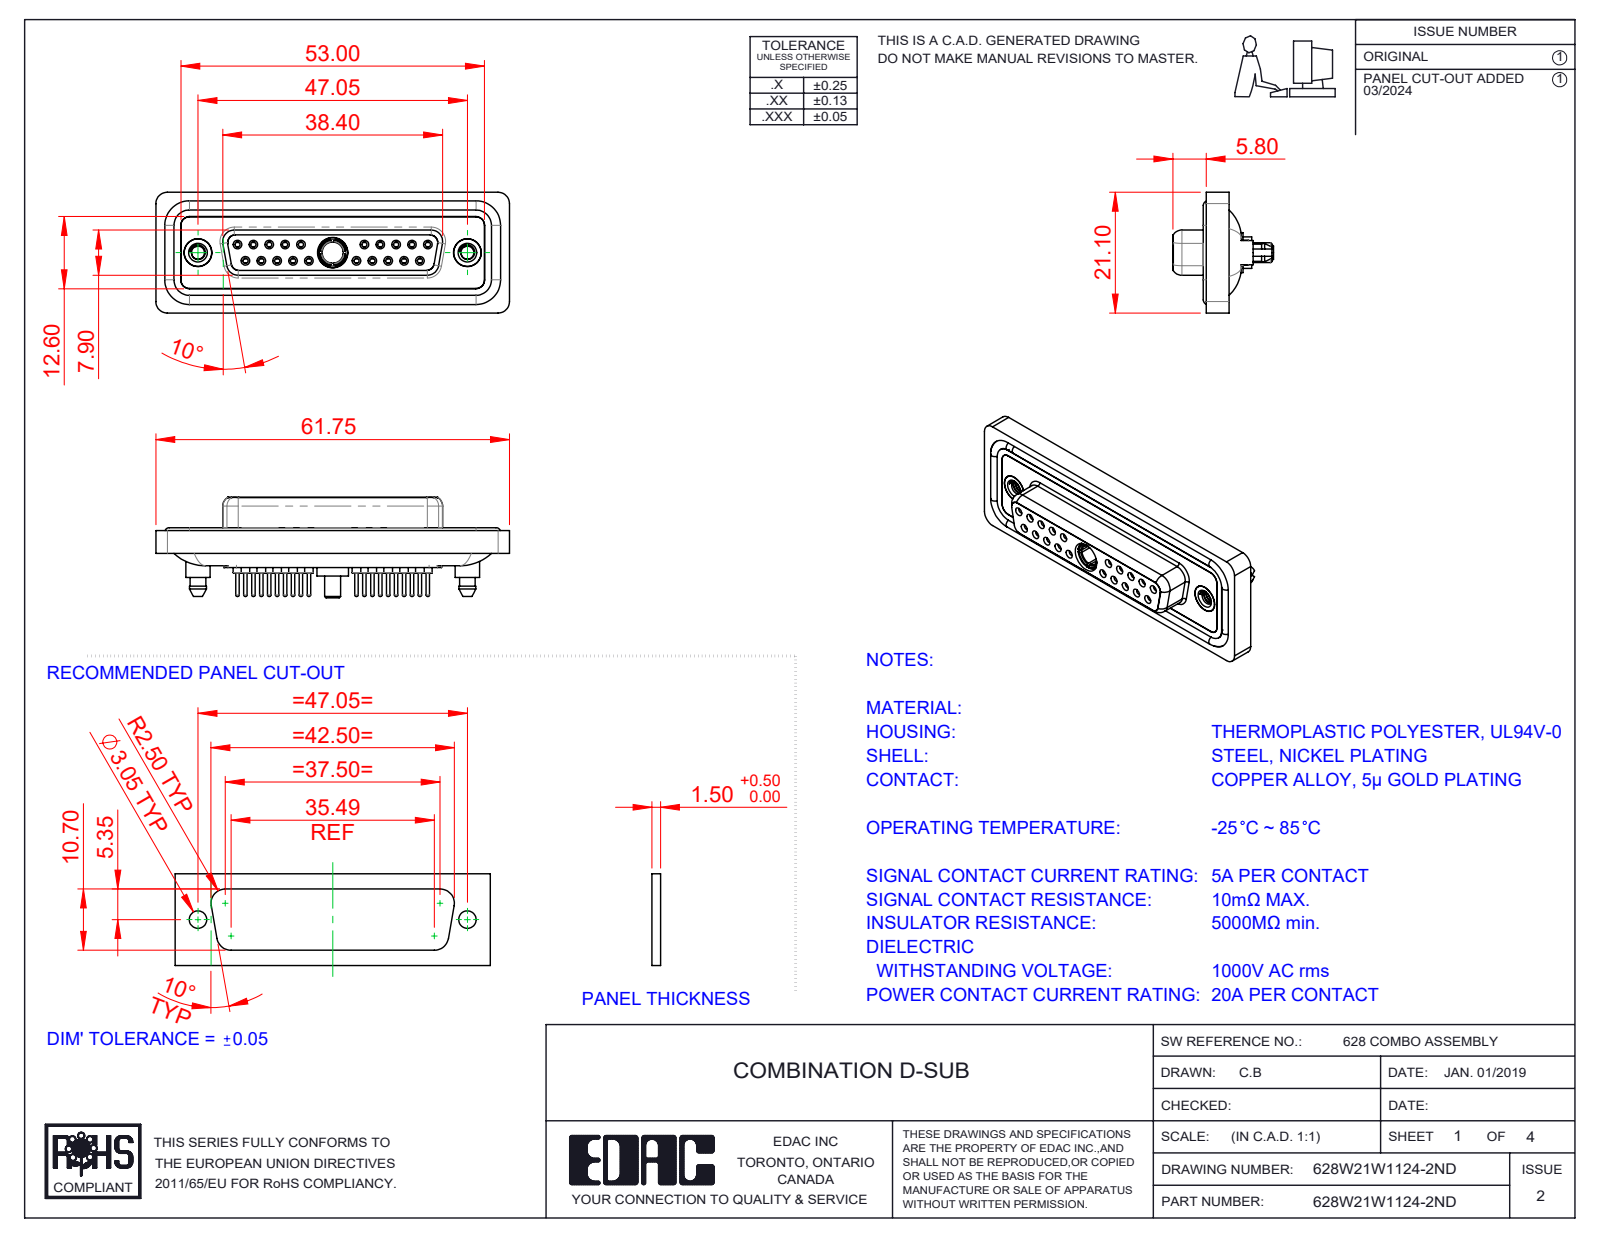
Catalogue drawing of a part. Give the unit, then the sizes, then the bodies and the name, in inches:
Units: inches
Overall size (bounding box): 2.431 × 0.831 × 0.691
Round holes (diameter × count): ⌀0.035 ×20, ⌀0.043 ×20, ⌀0.059 ×20, ⌀0.079 ×20, ⌀0.063 ×10, ⌀0.067 ×10, ⌀0.191 ×3, ⌀0.089 ×2, ⌀0.157 ×2, ⌀0.159 ×2, ⌀0.197 ×2, ⌀0.146 ×1
Round bosses / shafts (diameter × count): ⌀0.087 ×20, ⌀0.024 ×20, ⌀0.063 ×14, ⌀0.213 ×2, ⌀0.195 ×2, ⌀0.189 ×2, ⌀0.167 ×2, ⌀0.217 ×1
Partial cylindrical surfaces — rounded edges, fillets, slot ends (radius × count): R0.059 ×24, R0.079 ×18, R0.063 ×10, R0.053 ×8, R0.01 ×4, R0.02 ×4, R0.024 ×4, R0.026 ×4
Main face-to-face distances: 0.016, 0.071, 0.293, 0.26, 0.222, 0.063, 0.02, 0.278, 0.114, 0.043
Hole centre spacings: 0.124, 0.109, 0.218, 0.198, 0.327, 0.294, 0.654, 0.763
Volume: 0.519 in³ · Surface area: 22.23 in²
Bodies: 29 solids, 1626 faces (450 planar, 639 cylindrical, 537 other)
Part name (STEP PRODUCT): 628W21W1124-2ND; 628Combo Contact Row 2_24; 628Combo Housing_21W1; 628Combo Waterproof Housing_25 Contacts (+5 more)
STEP written by: SolidWorks 2023 (CONFIG_CONTROL_DESIGN)
